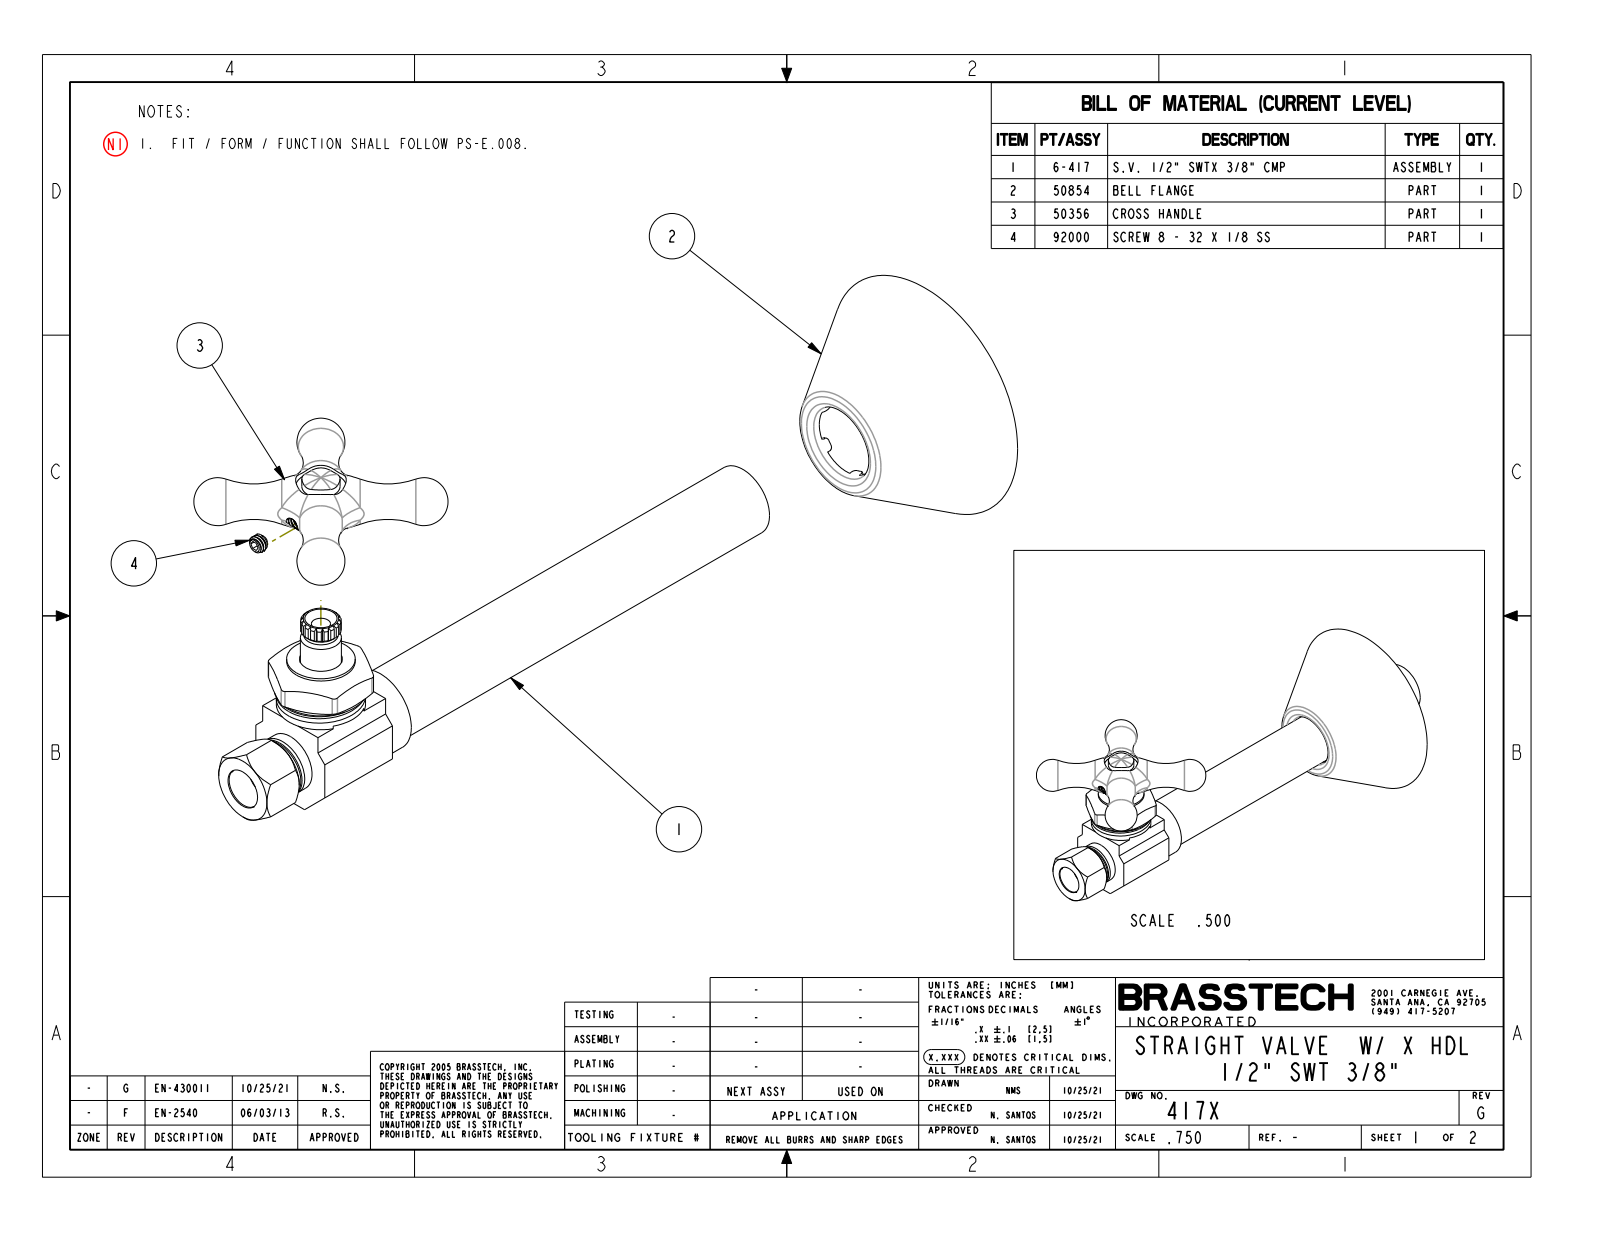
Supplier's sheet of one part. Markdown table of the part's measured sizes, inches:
| quantity | value |
| --- | --- |
| part name | 417X |
| STEP written by | CREO PARAMETRIC BY PTC INC, 2018500 (CONFIG_CONTROL_DESIGN) |
| units | inches |
| bodies | 2 solids, 583 faces (184 planar, 169 cylindrical, 230 other) |
| overall size | 6.483 × 2.723 × 2.4 |
| volume | 2.764 in³ |
| surface area | 45 in² |
| round holes (diameter × count) | 0.13 × 1, 0.175 × 1, 0.315 × 1, 0.376 × 1, 0.38 × 1, 0.382 × 1, 0.392 × 1, 0.4 × 1, 0.464 × 1, 0.5 × 1, 0.53 × 1 |
| round bosses / shafts (diameter × count) | 0.86 × 1, 0.818 × 1, 0.803 × 1, 0.69 × 1, 0.635 × 1, 0.629 × 1, 0.563 × 1, 0.37 × 1 |
| partial cylindrical surfaces (radius × count) | 0.01 × 18, 0.05 × 6, 0.142 × 1, 0.17 × 1, 0.184 × 1, 0.186 × 1, 0.187 × 1, 0.239 × 1 |
| main face-to-face distances | 0.625, 0.76, 0.135, 0.895, 0.045, 0.806, 0.616, 0.09, 0.67, 5.219 |
| hole center spacings | 1.187 |
